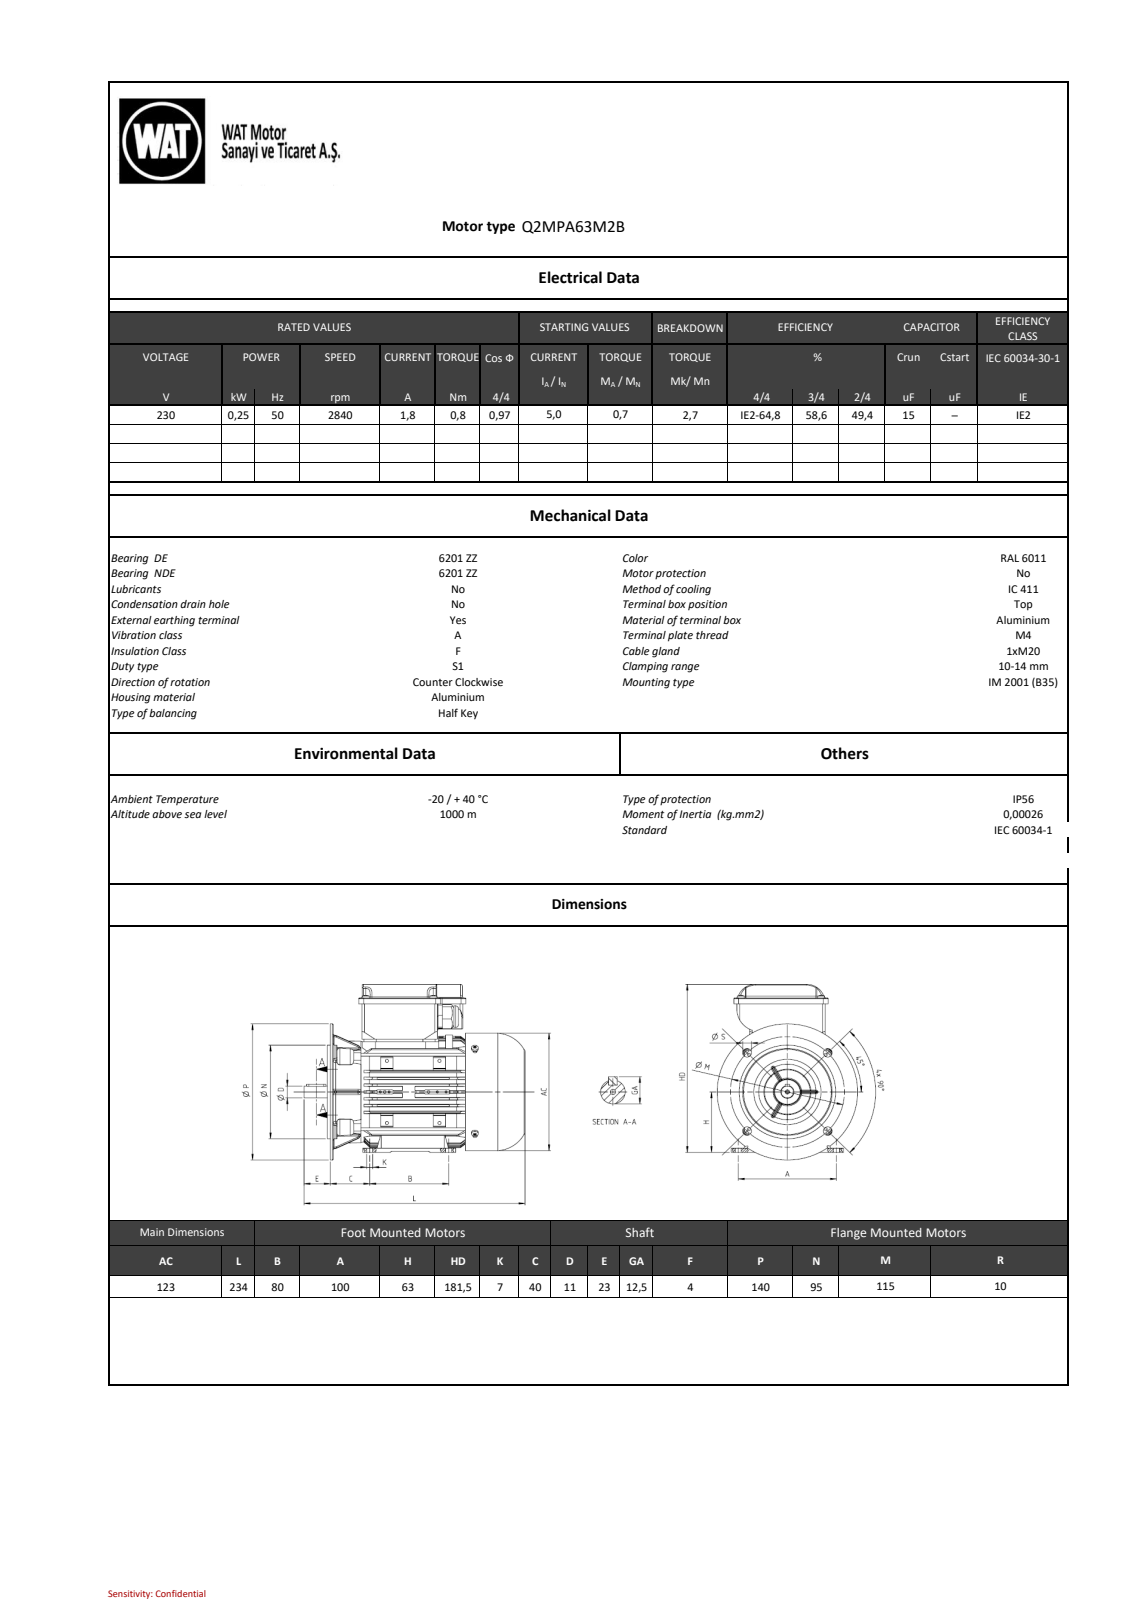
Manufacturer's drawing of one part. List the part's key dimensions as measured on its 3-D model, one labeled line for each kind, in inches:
Part name (STEP PRODUCT): BY6434017xx_004-TK_QM63-80; BY6424130xx_004-TKK_QM63-80; BY6434010xx_005-MOTOR_KAPAGI_QS63_FA_ISLEME; BY6423003xx_006-FAN_KAPAGI_QS63 (+8 more)
STEP written by: SIEMENS PLM Software NX2206.8101 (AUTOMOTIVE_DESIGN)
Units: inches
Bodies: 36 solids, 2376 faces (1192 planar, 789 cylindrical, 395 other)
Overall size (bounding box): 9.192 × 7.425 × 5.52
Volume: 41.52 in³ · Surface area: 691.3 in²
Round holes (diameter × count): ⌀0.144 ×10, ⌀0.157 ×8, ⌀0.177 ×8, ⌀0.394 ×8, ⌀0.098 ×6, ⌀0.13 ×5, ⌀0.165 ×4, ⌀0.183 ×4, ⌀0.189 ×4, ⌀0.118 ×3, ⌀0.276 ×2, ⌀0.197 ×1
Round bosses / shafts (diameter × count): ⌀0.315 ×8, ⌀0.157 ×8, ⌀0.118 ×8, ⌀0.189 ×4, ⌀5.52 ×1, ⌀4.843 ×1, ⌀3.74 ×1, ⌀0.995 ×1
Partial cylindrical surfaces — rounded edges, fillets, slot ends (radius × count): R0.02 ×212, R0.039 ×111, R0.079 ×56, R0.197 ×27, R0.098 ×20, R0.118 ×9, R0.217 ×9, R0.059 ×8
Main face-to-face distances: 0.118, 0.039, 0.177, 0.276, 1.101, 0.157, 7.146, 0.098, 0.138, 0.059
Hole centre spacings: 1.69, 3.122, 4.072, 4.078, 2.165, 1.692, 1.733, 2.126
